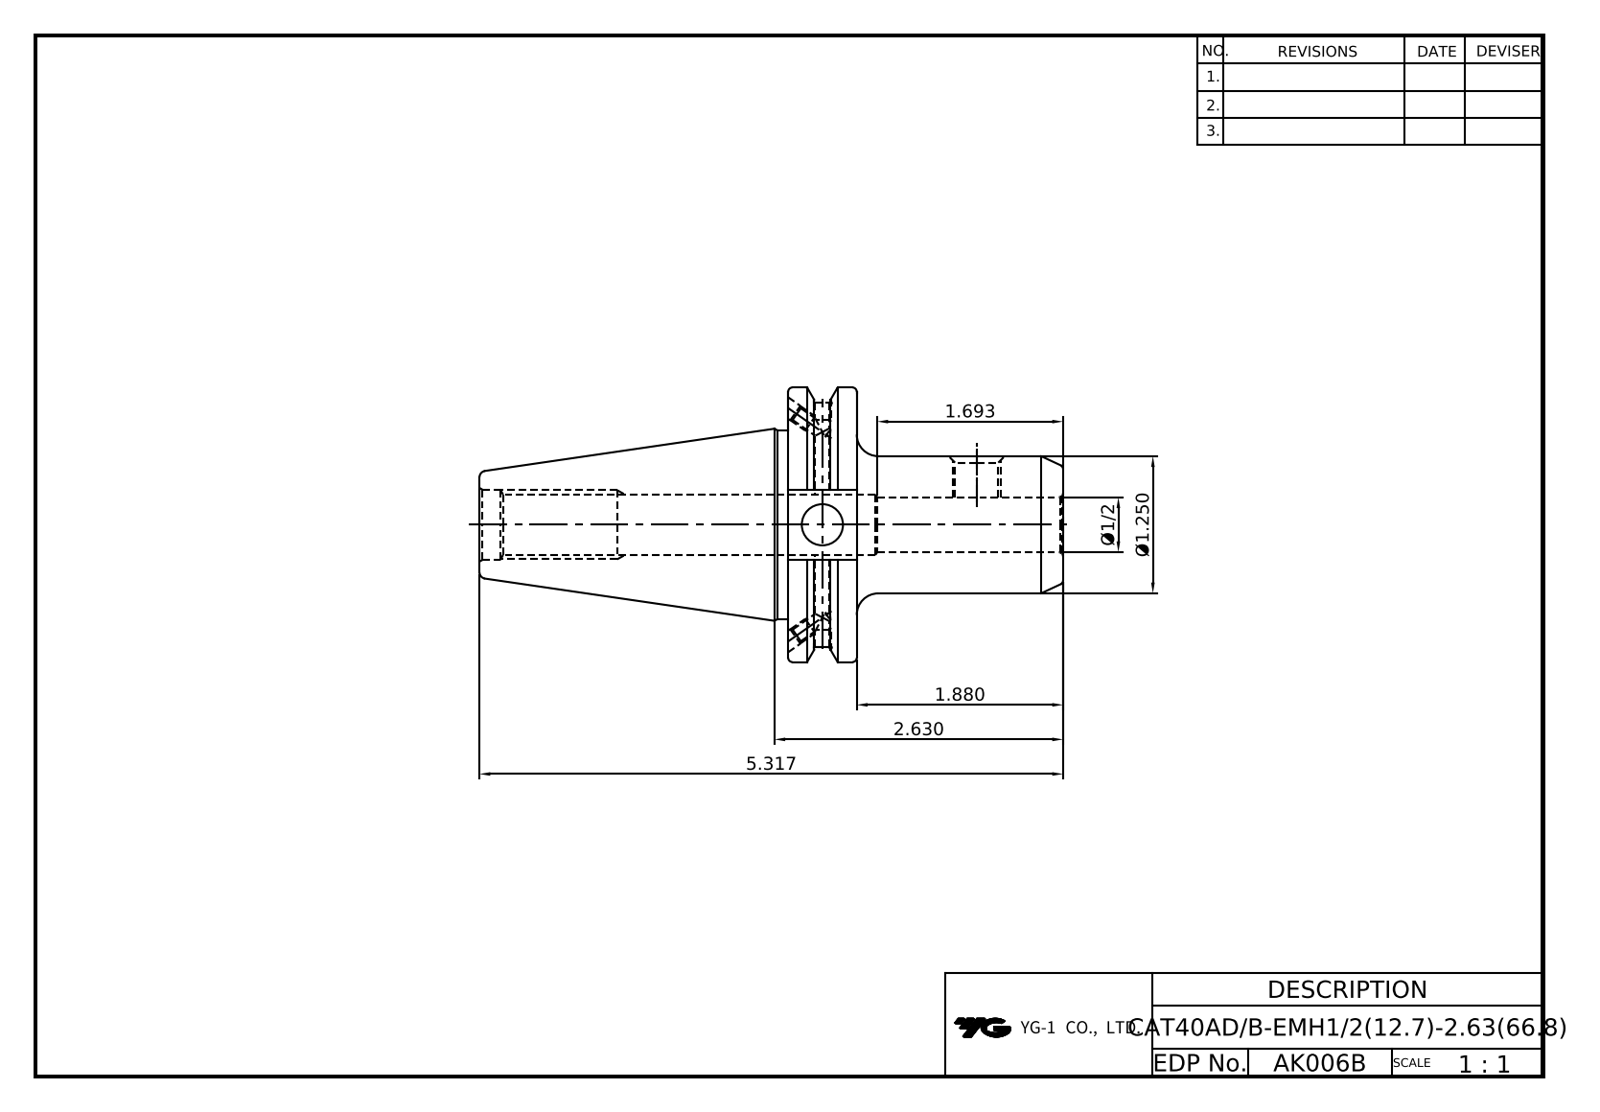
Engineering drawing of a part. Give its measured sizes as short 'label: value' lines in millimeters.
name: LO-CAT40ADB-EMH12.7-66.8
written by: Autodesk Inventor 2025 (AUTOMOTIVE_DESIGN)
unit: mm
bodies: 1 solid, 85 faces (35 planar, 27 cylindrical, 23 other)
size: 135.05 × 63.5 × 61.09
volume: 130 818 mm³; area: 27 291 mm²
holes: 4× ⌀3.24, 2× ⌀4, 2× ⌀4.2, 1× ⌀9.53, 1× ⌀9.73, 1× ⌀12.7, 1× ⌀13.39, 1× ⌀16.3
bosses: 1× ⌀63.5, 1× ⌀43.6, 1× ⌀31.75
rounds: 1× R28.15
face distances: 15.88, 63.63, 47.75, 47.6, 16.38, 71.42, 87.3, 135.05, 77.47, 6.05
